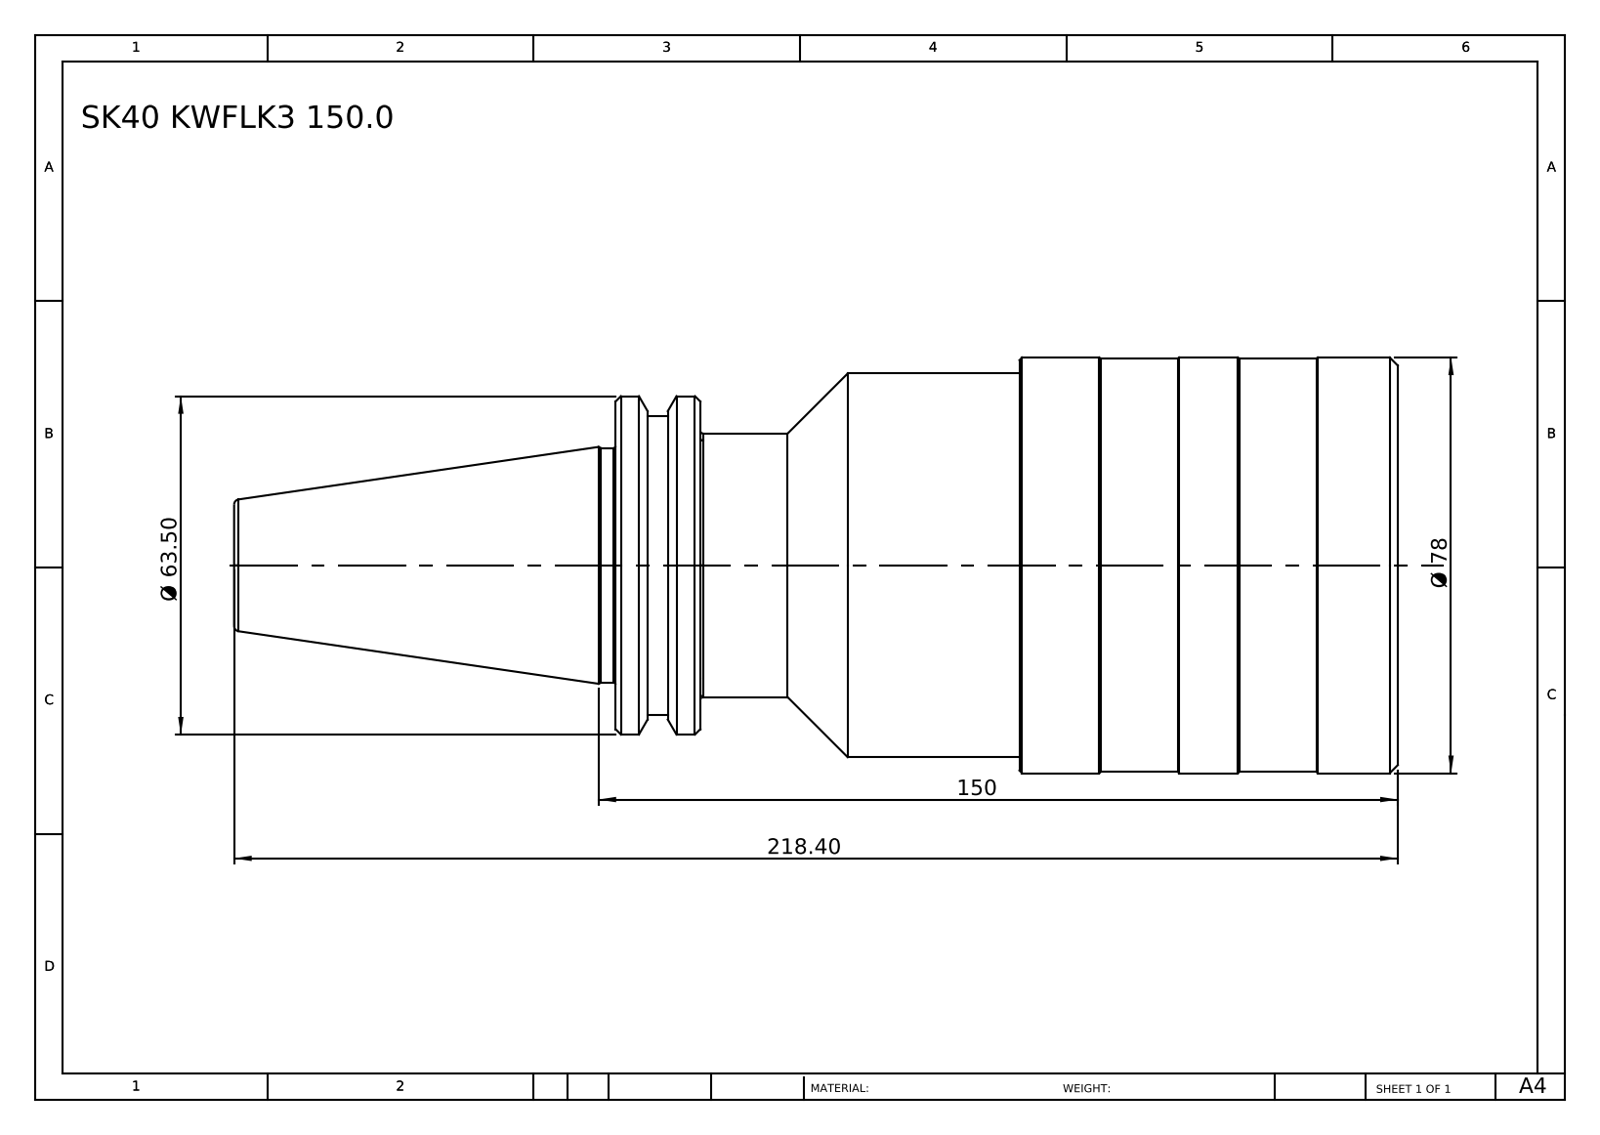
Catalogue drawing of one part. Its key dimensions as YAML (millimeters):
part_name: "SK40 KWFLK3 150.0"
step_written_by: "SolidWorks 2014 (CONFIG_CONTROL_DESIGN)"
units: millimeters
bodies: {solids: 1, faces: 64, planar: 7, cylindrical: 22, other: 35}
overall_size: [218.4, 78, 78]
volume: 650142
surface_area: 50517
round_bosses_or_shafts:
  - {diameter: 78, count: 1}
  - {diameter: 77.5, count: 1}
  - {diameter: 72, count: 1}
  - {diameter: 63.5, count: 1}
  - {diameter: 56, count: 1}
  - {diameter: 49.5, count: 1}
  - {diameter: 44, count: 1}
face_to_face_distances: [146.8, 130.9, 15.9, 71, 59.9, 75.8, 218.4, 147.4, 87.5, 71.6]
